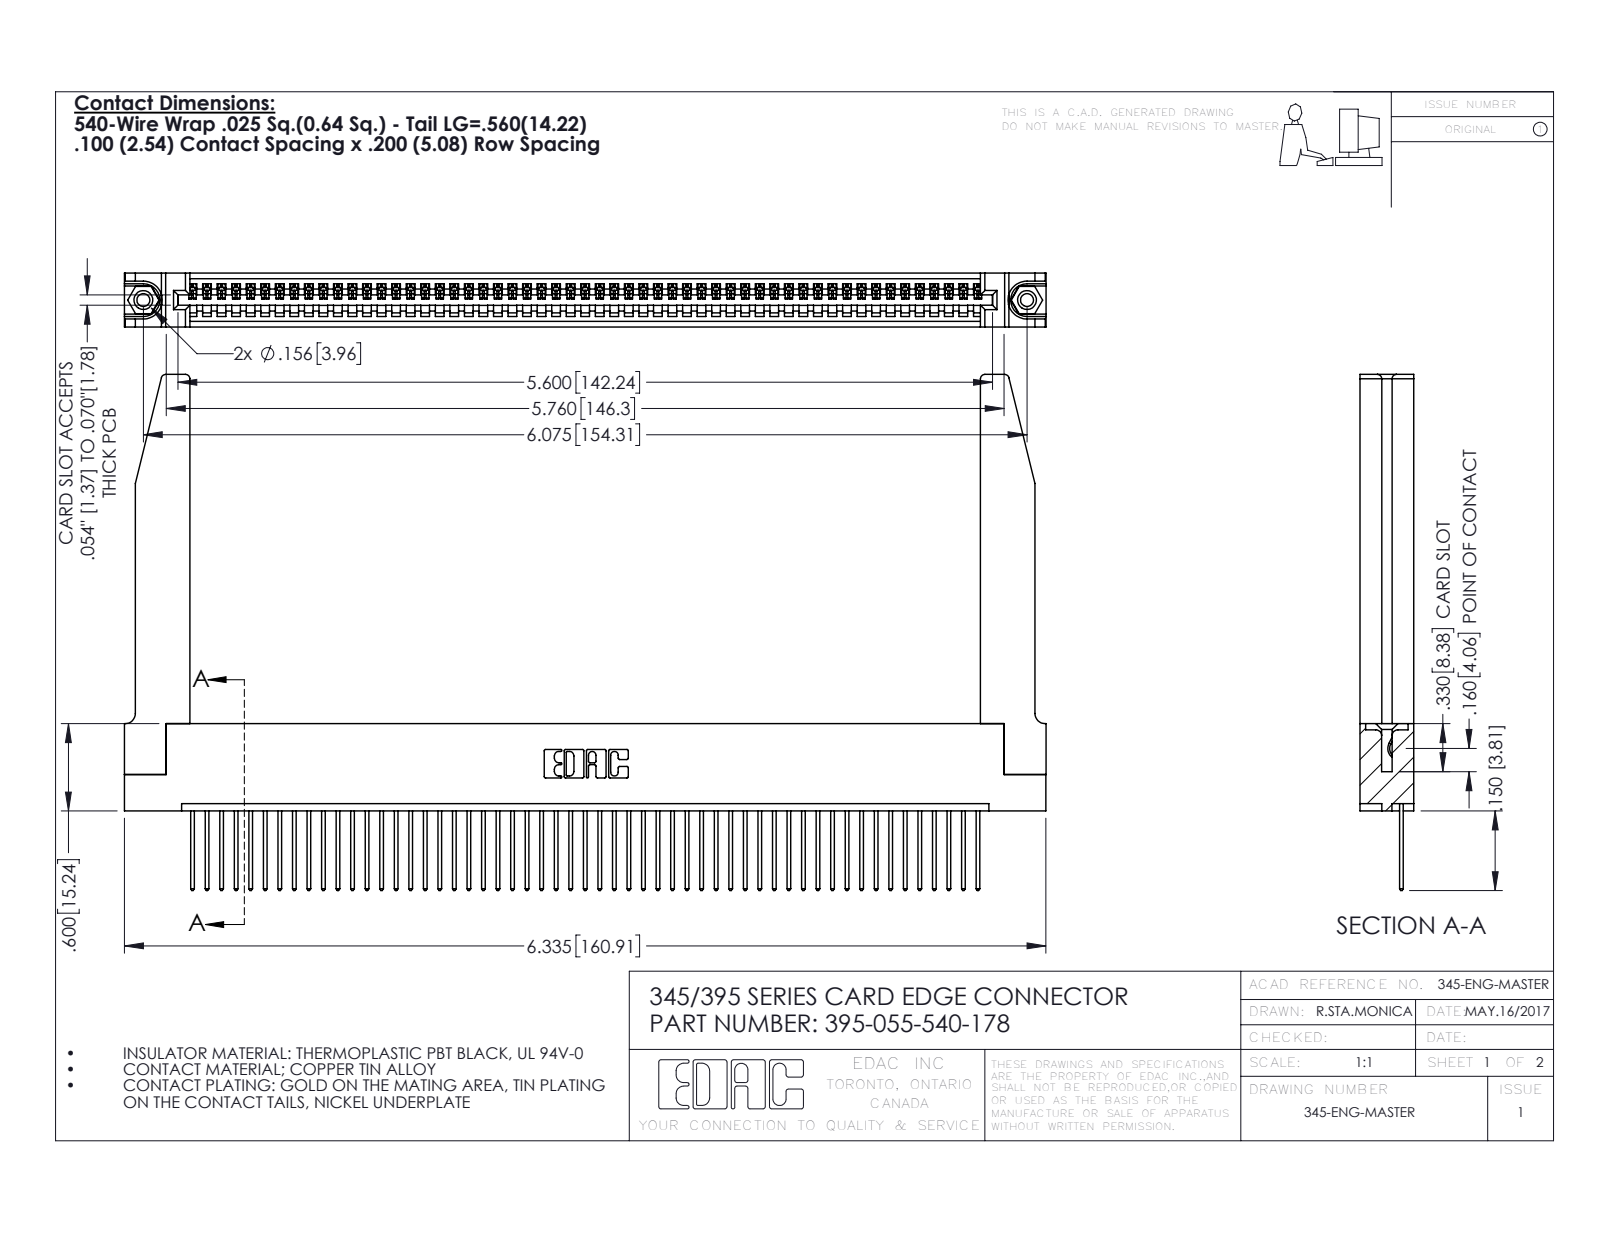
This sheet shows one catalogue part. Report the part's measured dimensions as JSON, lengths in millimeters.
{"part_name": "345-292-001_345-293-140; 395-055-540-178; 345-220-078_345-220-078; 345-250-001_345-250-001-102 (+1 more)", "step_written_by": "SolidWorks 2016 (CONFIG_CONTROL_DESIGN)", "units": "millimeters", "bodies": {"solids": 60, "faces": 3550, "planar": 2422, "cylindrical": 1076, "other": 52}, "overall_size": [160.9, 90.1, 9.4], "volume_mm3": 23240, "surface_area_mm2": 28110, "round_holes": [[2.3, 2], [3.2, 2], [4, 2], [1.6, 1]], "round_bosses_or_shafts": [[3.9, 2]], "partial_cylinders_radius": [[0.2, 110], [0.3, 110], [0.3, 22], [0.8, 8], [0.2, 6], [0.8, 6], [0.7, 3], [0.8, 2]], "face_to_face_distances": [1.8, 9.4, 7.6, 2.5, 6.9, 0.6, 5.1, 5.7, 3.8, 3.8], "hole_center_spacings": [6.9, 148.3, 154.3]}
